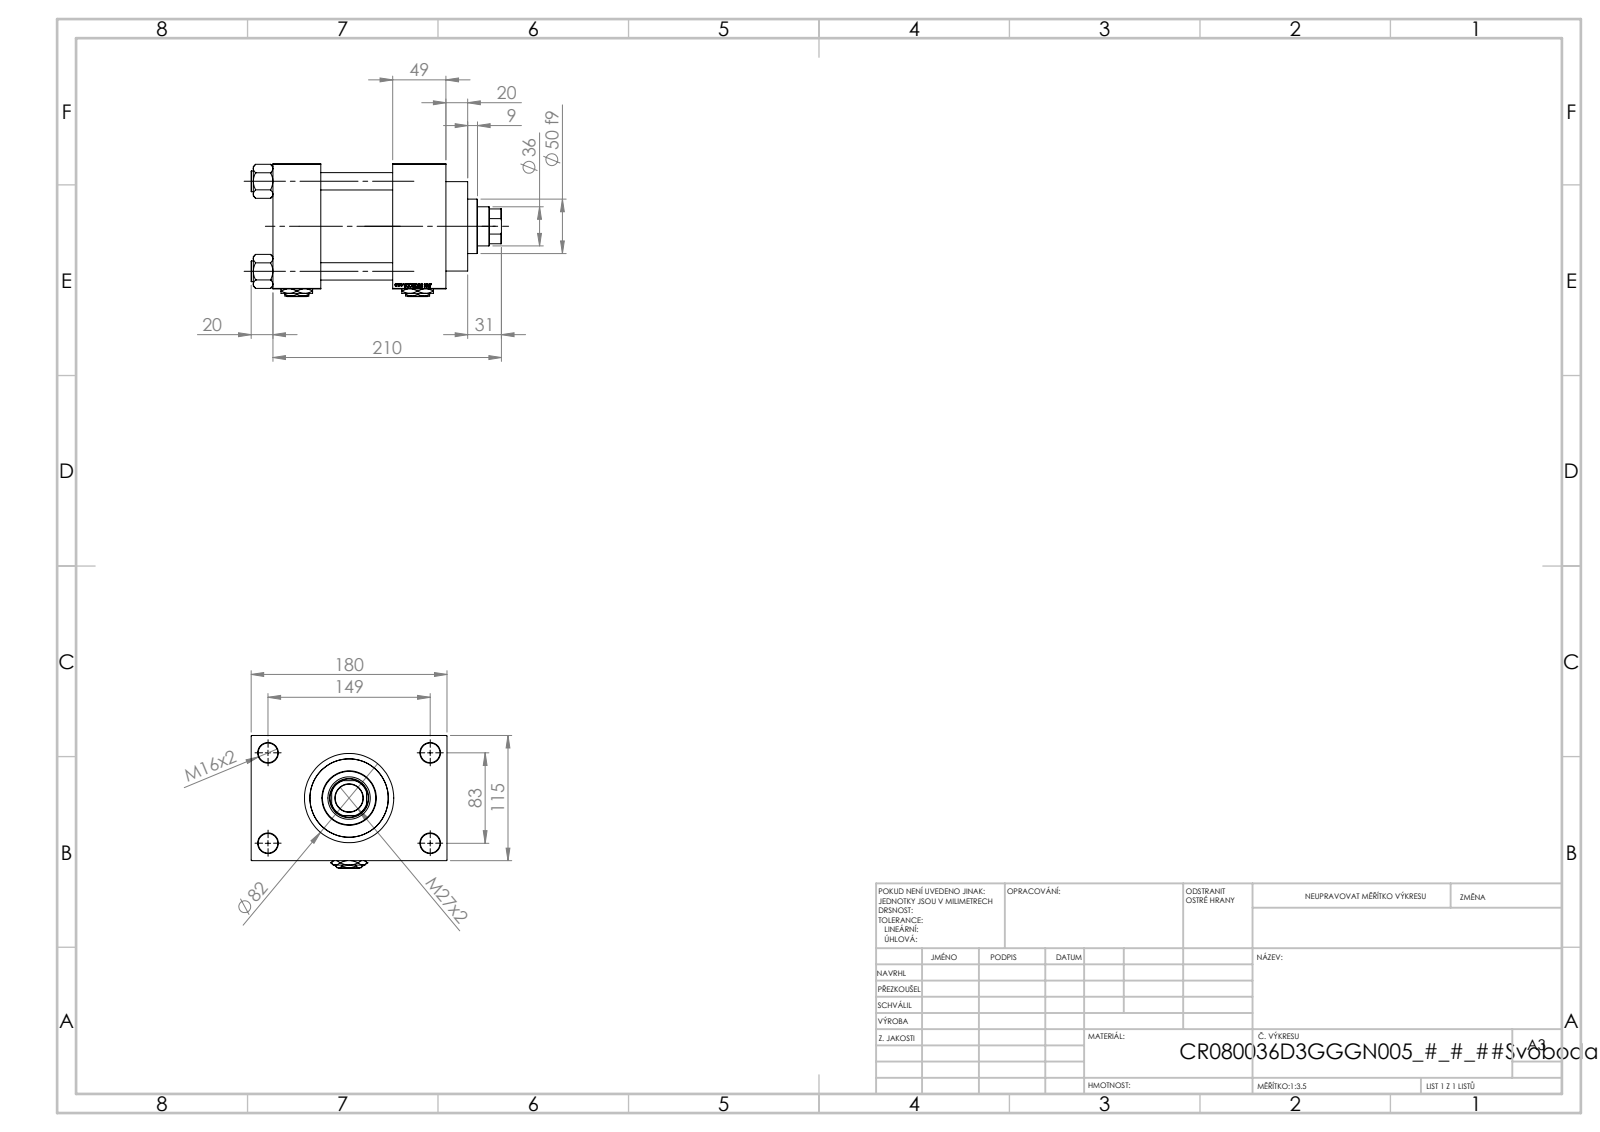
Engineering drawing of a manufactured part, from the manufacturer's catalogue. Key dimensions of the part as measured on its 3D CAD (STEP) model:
Part name (STEP PRODUCT): V215CR_VCP_D; V215CR_D_TYCINKA; Zatka_pro_OIL_PORT; V215_VC_A (+2 more)
STEP written by: SolidWorks 2019 (CONFIG_CONTROL_DESIGN)
Units: millimetres
Bodies: 13 solids, 1253 faces (593 planar, 100 cylindrical, 560 other)
Overall size (bounding box): 230 × 180 × 122
Volume: 1 983 000 mm³ · Surface area: 300 614 mm²
Round holes (diameter × count): ⌀16 ×4, ⌀18 ×4, ⌀7 ×2, ⌀26.44 ×2, ⌀35 ×2, ⌀25.5 ×1, ⌀36 ×1, ⌀39 ×1, ⌀61 ×1, ⌀72 ×1, ⌀80 ×1
Round bosses / shafts (diameter × count): ⌀19 ×4, ⌀86 ×1, ⌀82 ×1, ⌀50 ×1
Partial cylindrical surfaces — rounded edges, fillets, slot ends (radius × count): R17.5 ×1
Main face-to-face distances: 115, 66, 110, 49, 44, 159, 147.5, 32.5, 20, 69
Hole centre spacings: 33.15, 58.48, 82.7, 85.28, 89.24, 115.85, 142.43, 83
